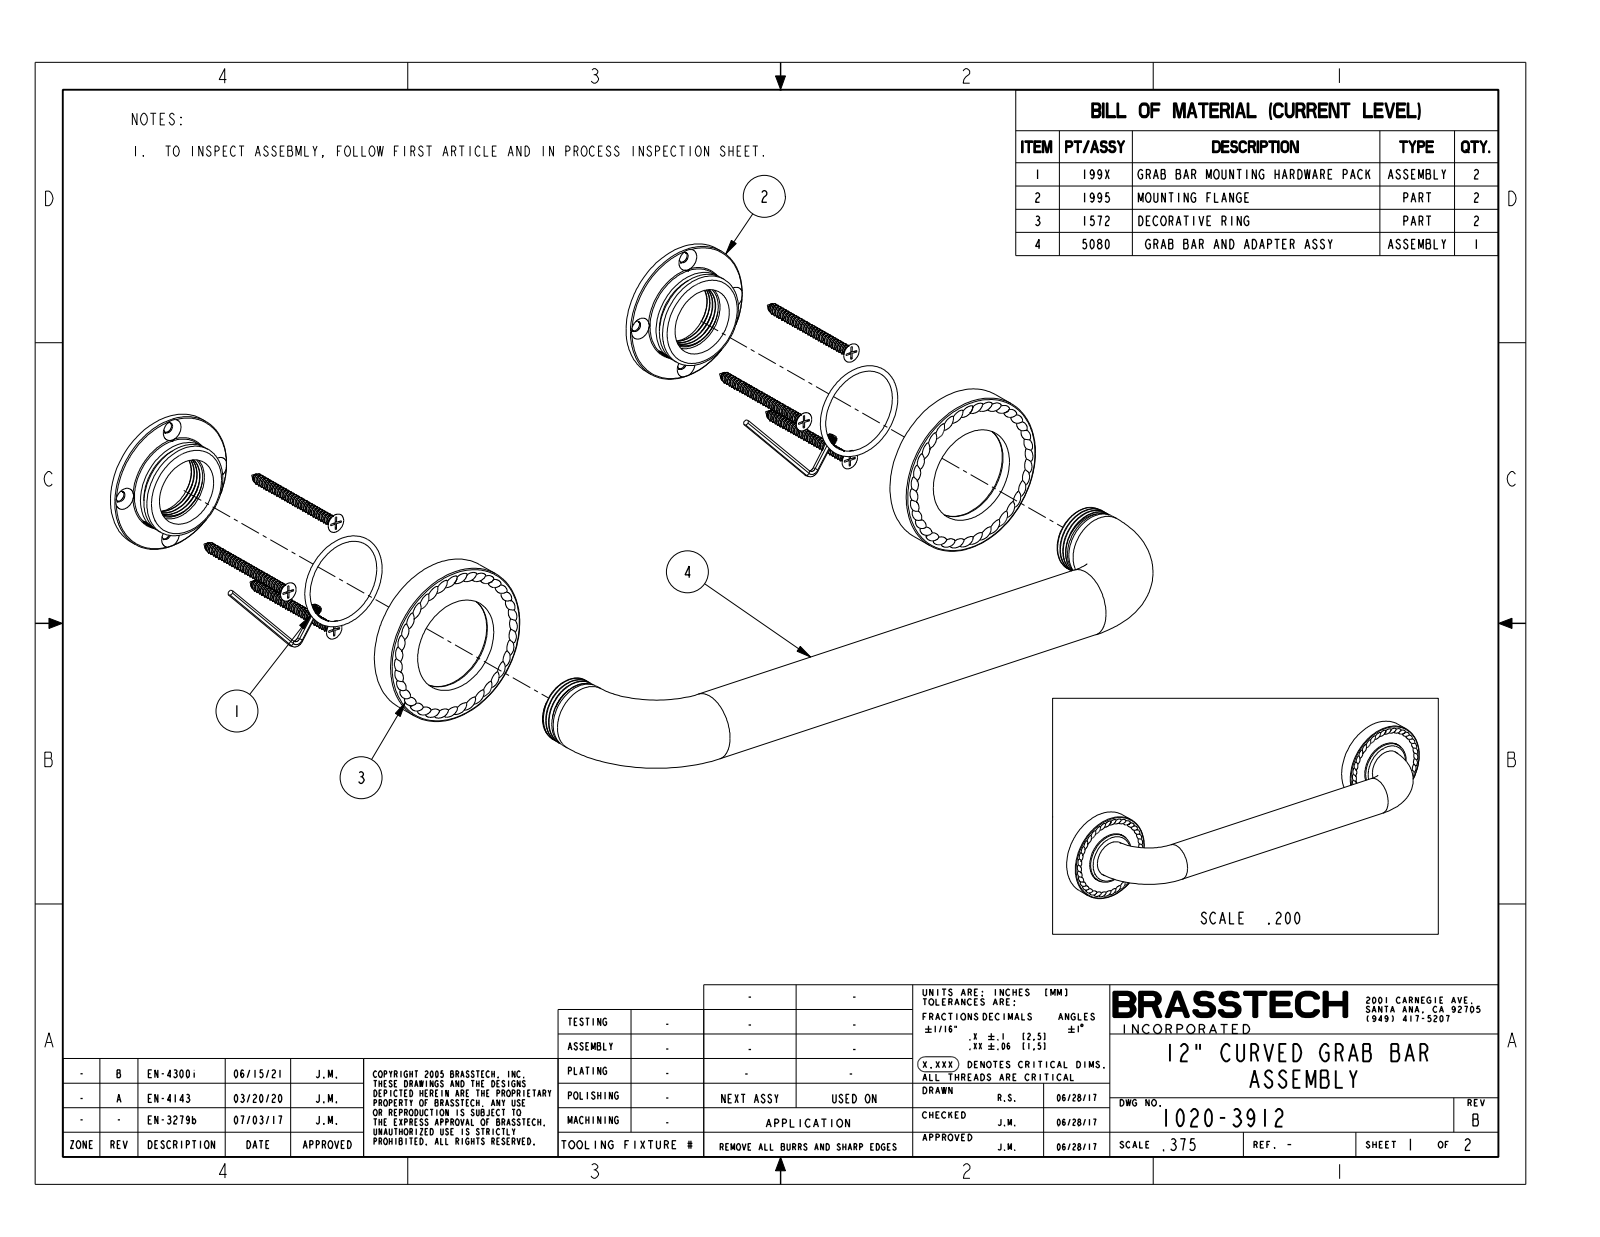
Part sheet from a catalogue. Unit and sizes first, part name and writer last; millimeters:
Units: millimetres
Overall size (bounding box): 381 × 76.2 × 69.9
Round holes (diameter × count): ⌀5.1 ×8, ⌀29.3 ×3, ⌀4.1 ×2, ⌀22 ×2, ⌀29.5 ×2, ⌀32 ×2, ⌀45 ×2, ⌀72.2 ×2
Round bosses / shafts (diameter × count): ⌀31.8 ×3, ⌀76.2 ×2, ⌀66 ×2, ⌀49 ×2, ⌀44.5 ×2, ⌀40.5 ×2, ⌀31.4 ×2, ⌀29.1 ×2
Partial cylindrical surfaces — rounded edges, fillets, slot ends (radius × count): R5.4 ×8, R1 ×2
Main face-to-face distances: 12.7, 10.7, 2, 3.8, 8.9, 2.5, 11.4, 6.9, 15.2, 4.6
Hole centre spacings: 27.6, 39.1, 304.8, 55.2, 278.6, 306, 333.6, 277.2
Volume: 113 000 mm³ · Surface area: 178 800 mm²
Bodies: 9 solids, 772 faces (152 planar, 188 cylindrical, 432 other)
Part name (STEP PRODUCT): 91496; 1995; 20-287_ASM; 50869 (+4 more)
STEP written by: PRO/ENGINEER BY PARAMETRIC TECHNOLOGY CORPORATION, 2013150 (CONFIG_CONTROL_DESIGN)
